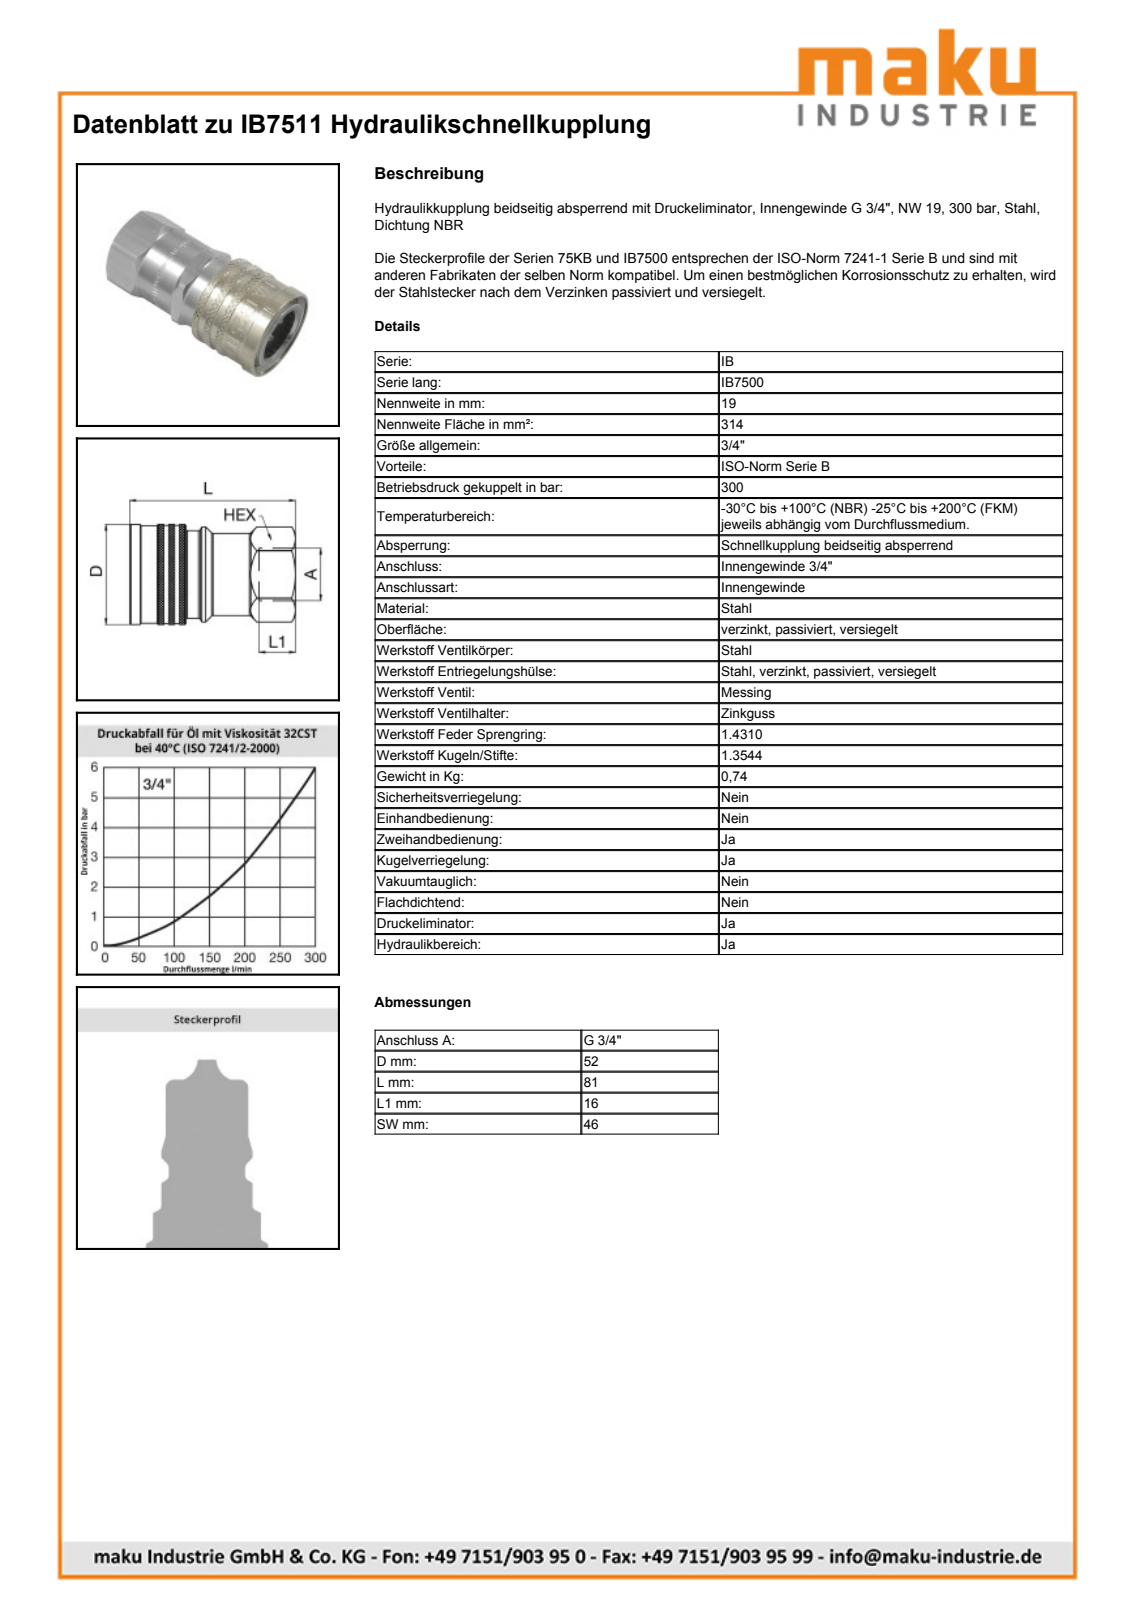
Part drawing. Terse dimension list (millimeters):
name: IB7511
written by: SolidWorks 2009 (AUTOMOTIVE_DESIGN)
unit: mm
bodies: 1 solid, 281 faces (34 planar, 88 cylindrical, 159 other)
size: 81 × 52 × 52
volume: 113 626 mm³; area: 26 035 mm²
holes: 2× ⌀1, 1× ⌀2.85, 1× ⌀3.93, 1× ⌀19, 1× ⌀24.12, 1× ⌀31.5, 1× ⌀32.5, 1× ⌀32.8, 1× ⌀35.32, 1× ⌀41.7, 1× ⌀45.7, 1× ⌀46.2
bosses: 1× ⌀52, 1× ⌀51.2, 1× ⌀51, 1× ⌀46, 1× ⌀45.6, 1× ⌀41.5, 1× ⌀2.75
rounds: 1× R16.69, 1× R19.75, 1× R25
face distances: 46, 15.25, 47, 31.75, 81, 65.75, 34, 5.35, 52.35, 37.1
